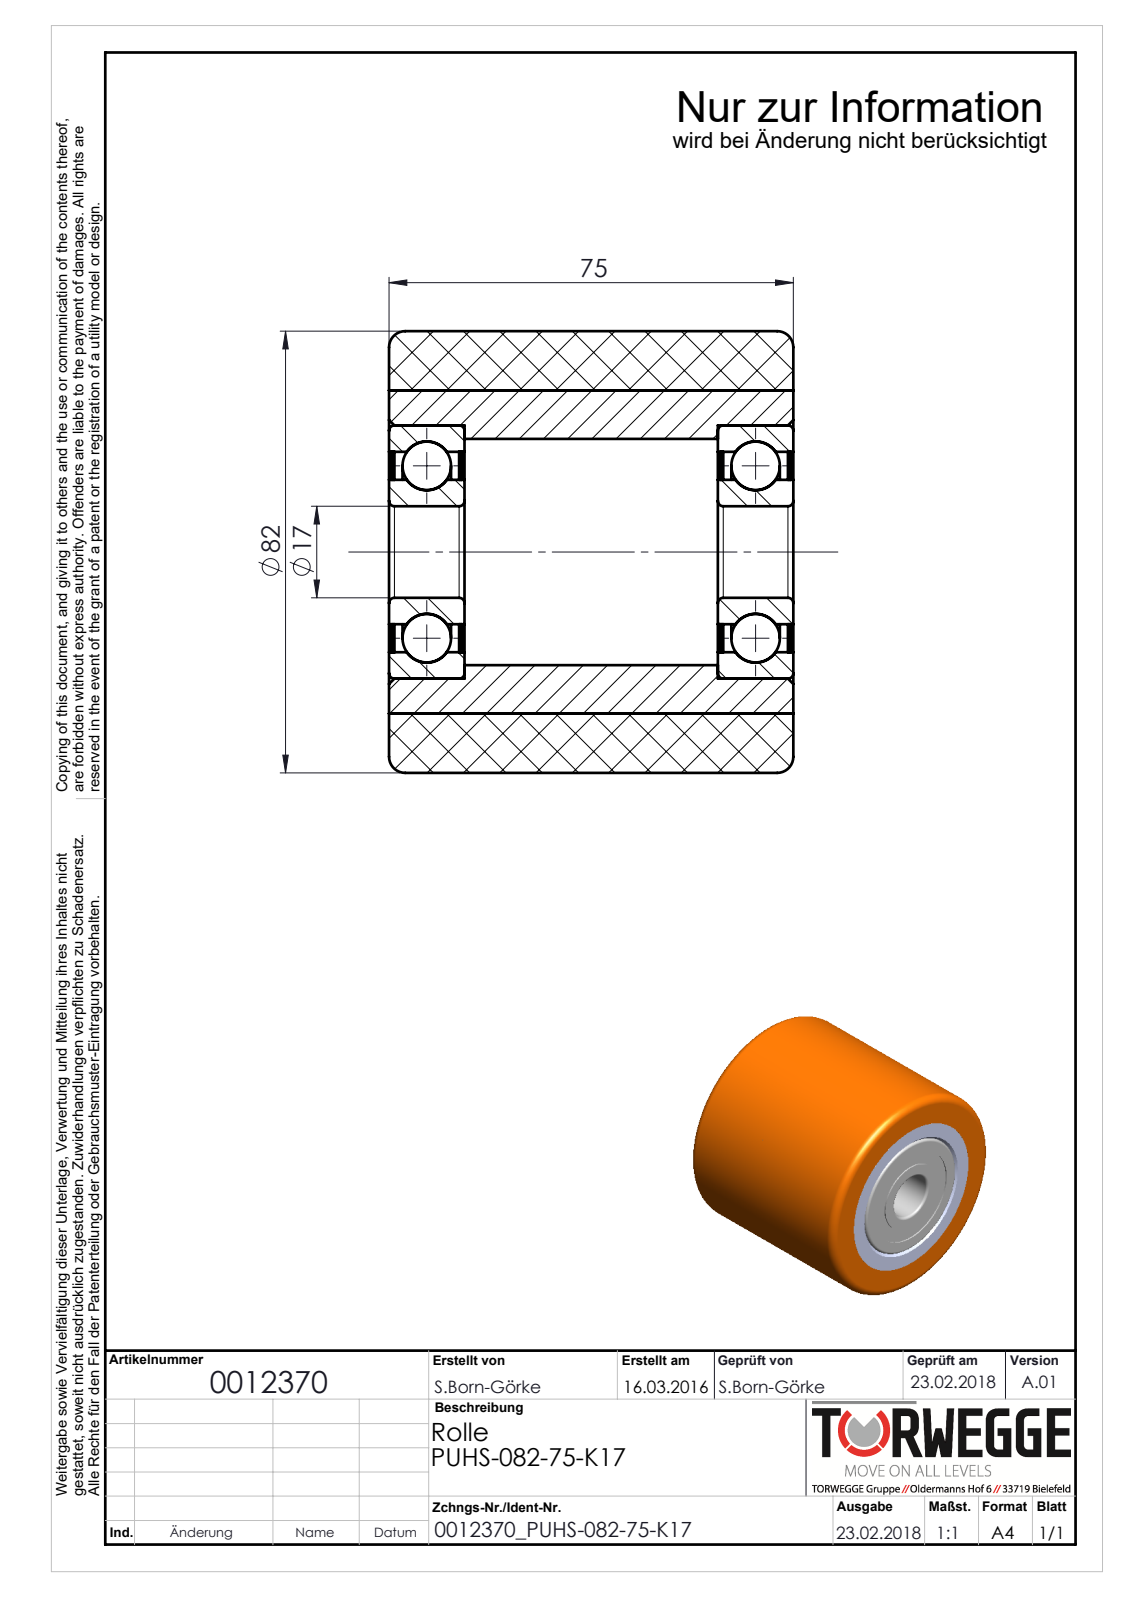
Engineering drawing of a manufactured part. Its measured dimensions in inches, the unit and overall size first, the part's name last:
Units: inches
Overall size (bounding box): 3.228 × 3.228 × 2.953
Round holes (diameter × count): ⌀0.669 ×1, ⌀1.055 ×1, ⌀1.465 ×1, ⌀1.654 ×1, ⌀1.85 ×1, ⌀2.362 ×1
Round bosses / shafts (diameter × count): ⌀3.228 ×1
Main face-to-face distances: 2.402, 0.02, 2.953, 0.512, 0.551, 0.039, 0.531, 2.421, 0.492, 2.382
Volume: 19.42 in³ · Surface area: 140.3 in²
Bodies: 12 solids, 118 faces (22 planar, 52 cylindrical, 44 other)
Part name (STEP PRODUCT): 0012370_PUHS-082-75-K17
STEP written by: SolidWorks 2016 (AUTOMOTIVE_DESIGN)
